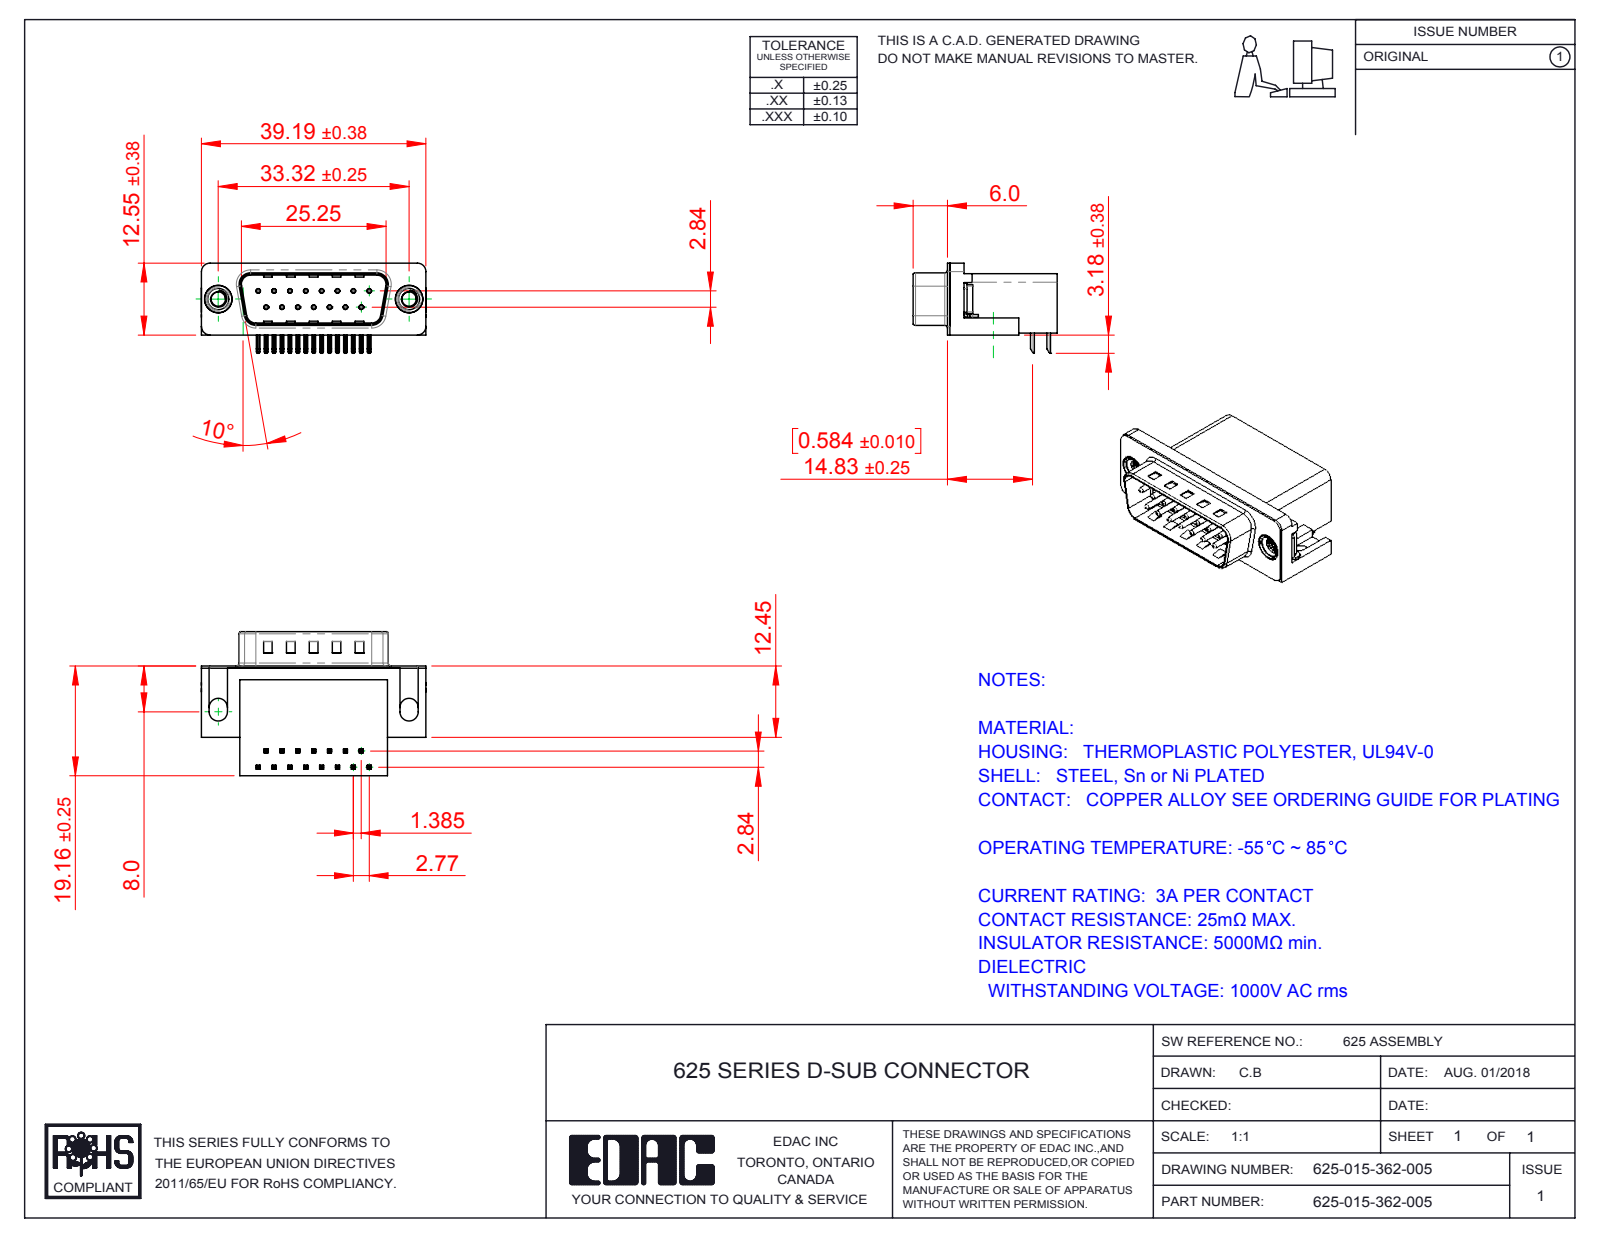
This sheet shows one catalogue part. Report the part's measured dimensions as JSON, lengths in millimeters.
{"part_name": "625 Contact Bottom; 625 Non Board Mount; 625 Contact Top; 625-015-362-005 (+3 more)", "step_written_by": "SolidWorks 2016 (CONFIG_CONTROL_DESIGN)", "units": "millimeters", "bodies": {"solids": 21, "faces": 1477, "planar": 895, "cylindrical": 447, "other": 135}, "overall_size": [39.22, 25.16, 15.73], "volume_mm3": 6210, "surface_area_mm2": 6294, "round_holes": [[0.35, 15], [0.8, 15], [2.5, 2], [4, 2], [4.8, 2], [5, 2]], "round_bosses_or_shafts": [[0.75, 15], [4.9, 2], [4.75, 2], [3.9, 2]], "partial_cylinders_radius": [[0.25, 68], [0.12, 30], [1, 16], [0.5, 9], [1.6, 8], [1.5, 6], [0.9, 4], [2, 4]], "face_to_face_distances": [0.4, 10.35, 18.76, 2.1, 10.46, 19.16, 1.7, 10.86, 8.76, 16.26], "hole_center_spacings": [3.16, 2.77, 5.54, 8.31, 11.08, 5.03, 5.04, 7.48]}
